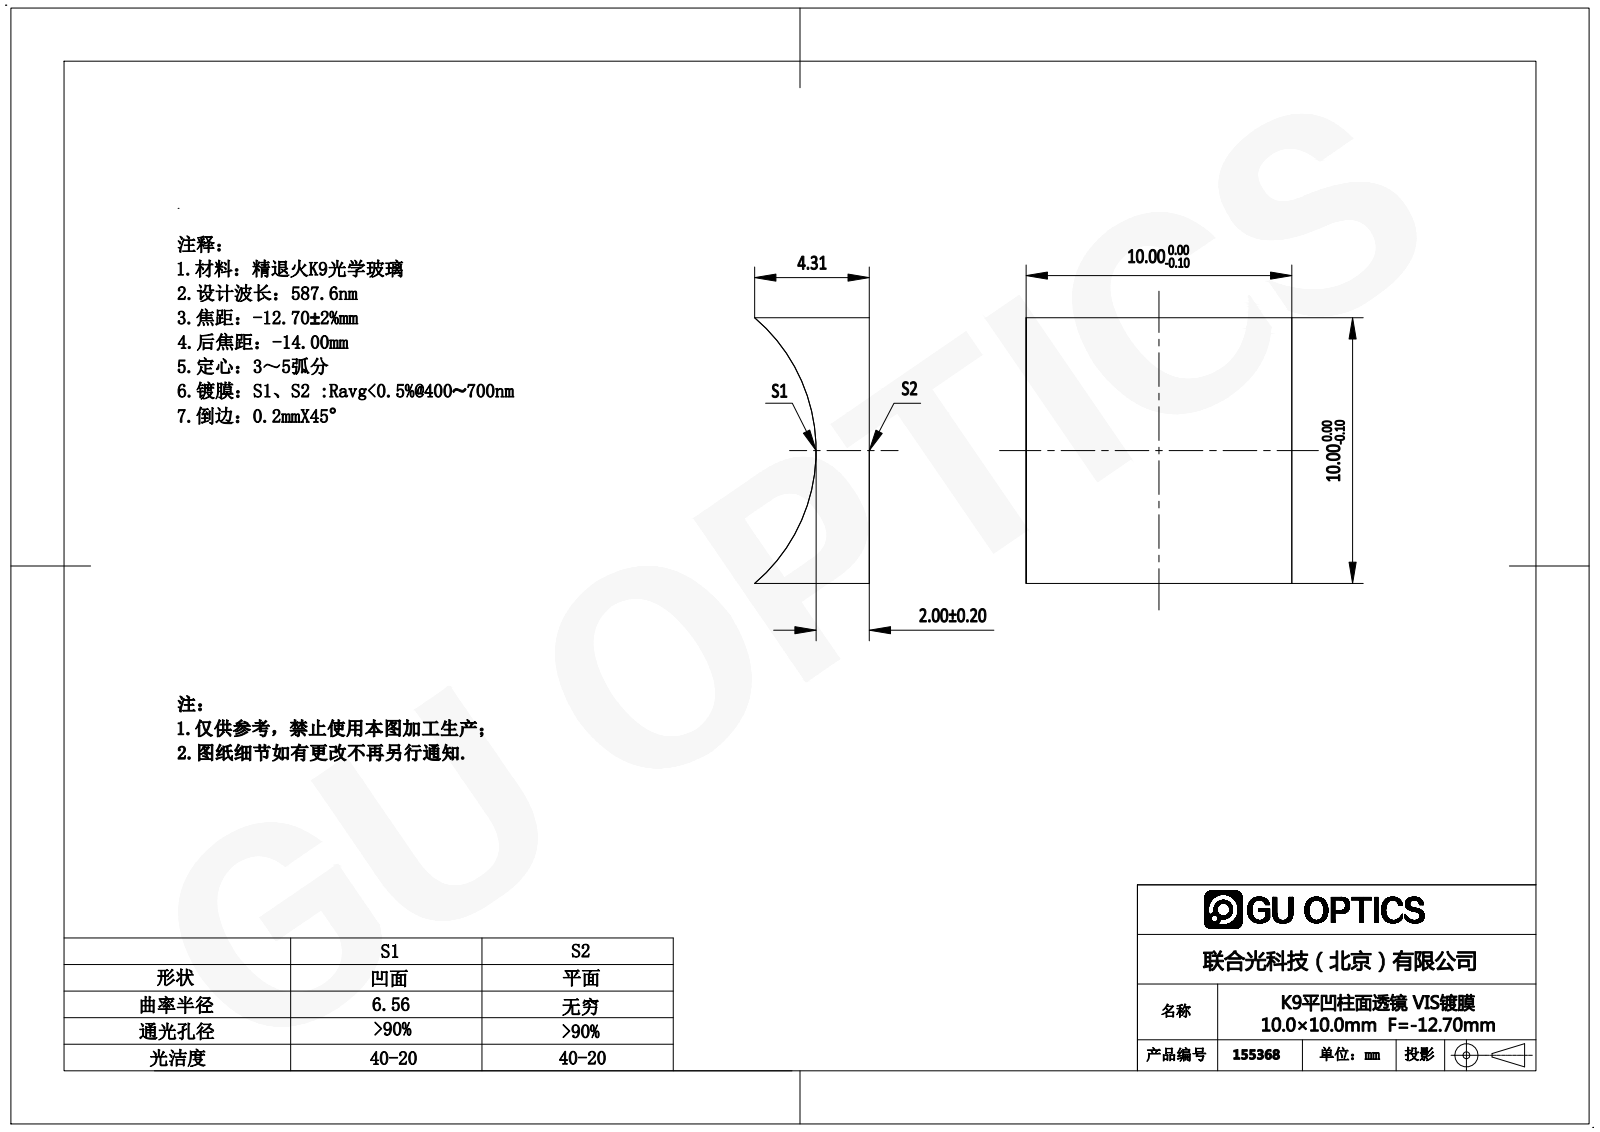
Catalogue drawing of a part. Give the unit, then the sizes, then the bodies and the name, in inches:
Units: inches
Overall size (bounding box): 0.394 × 0.394 × 0.17
Partial cylindrical surfaces — rounded edges, fillets, slot ends (radius × count): R0.258 ×1
Main face-to-face distances: 0.394
Volume: 0.017 in³ · Surface area: 0.549 in²
Bodies: 1 solid, 6 faces (5 planar, 1 cylindrical, 0 other)
Part name (STEP PRODUCT): 155335
STEP written by: SolidWorks 2016 (AUTOMOTIVE_DESIGN)
